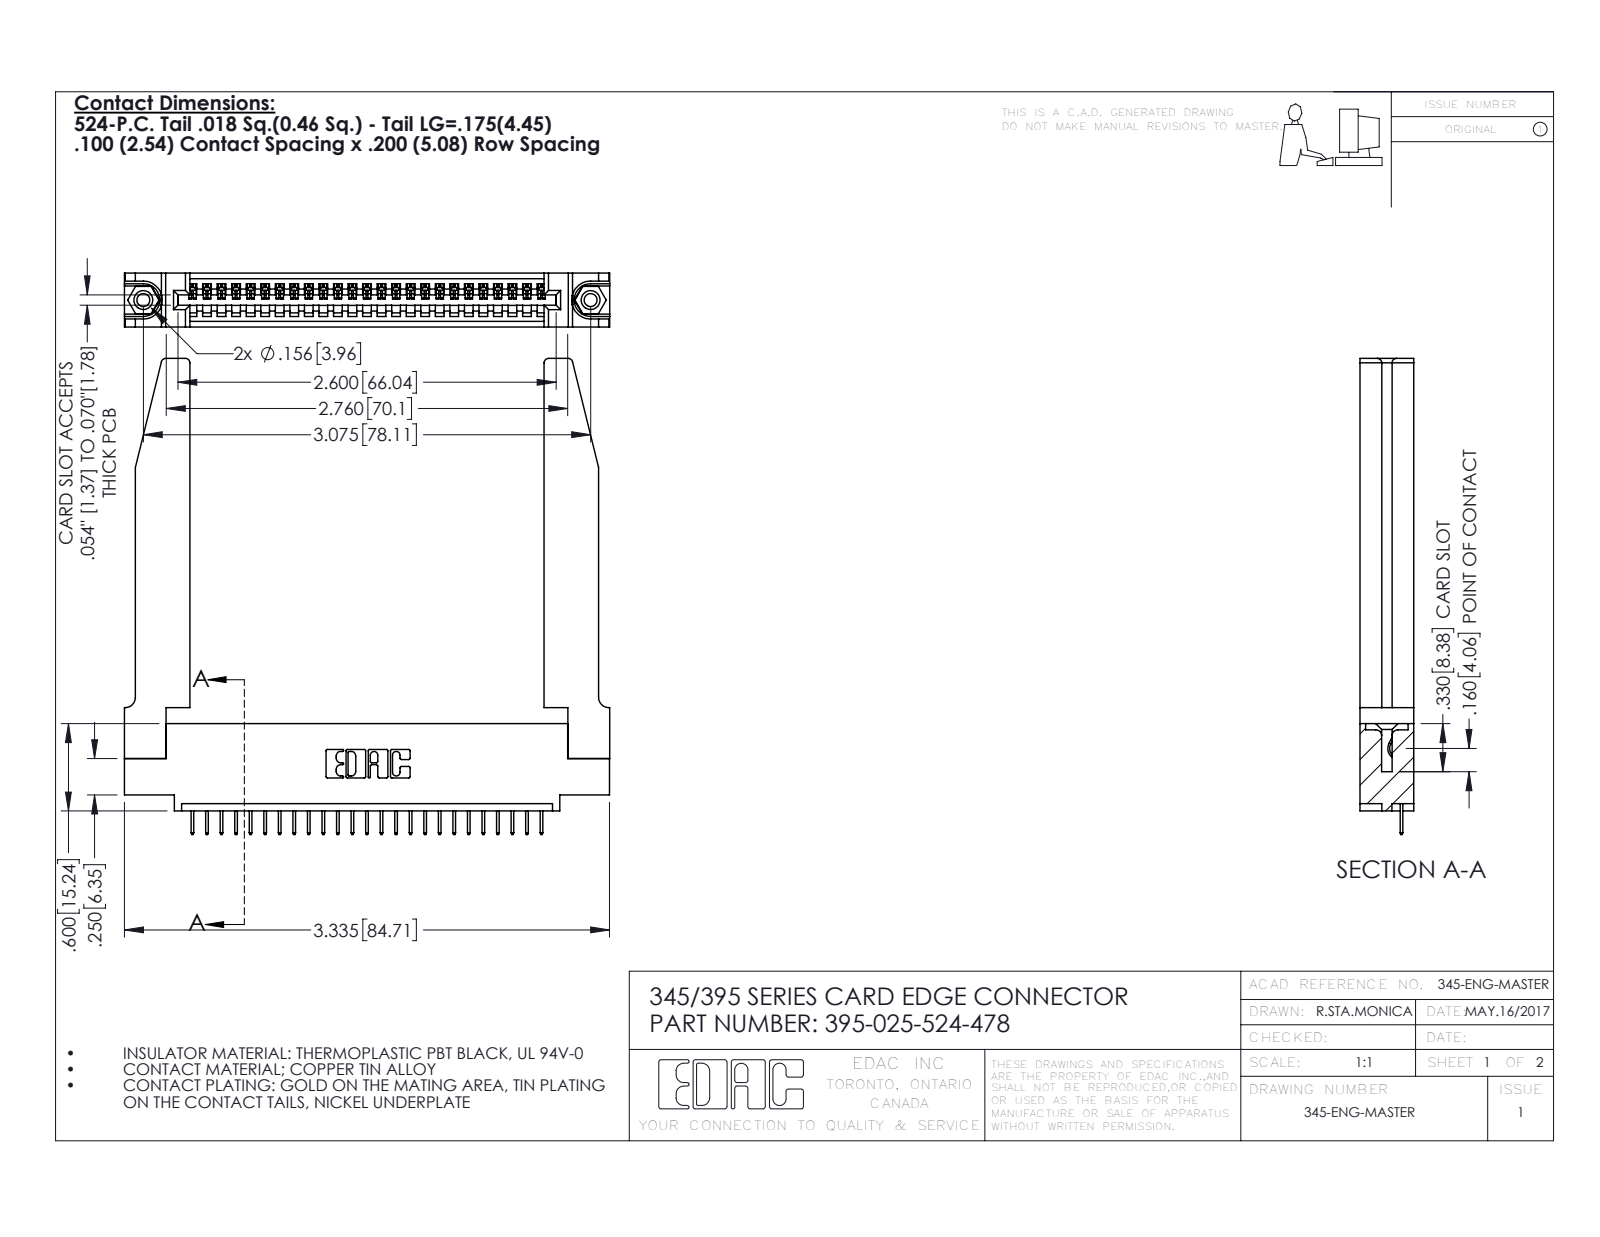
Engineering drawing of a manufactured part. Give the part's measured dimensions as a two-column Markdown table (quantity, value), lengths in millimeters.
| quantity | value |
| --- | --- |
| part name | 345-250-001_345-250-001-102; 345-220-078_345-220-078; 345-292-001_345-293-124; 345 Part_0.110 Offset - 0.156 Dia-TH (+1 more) |
| STEP written by | SolidWorks 2016 (CONFIG_CONTROL_DESIGN) |
| units | millimeters |
| bodies | 30 solids, 1914 faces (1376 planar, 486 cylindrical, 52 other) |
| overall size | 84.7 × 83.1 × 9.4 |
| volume | 15 500 mm³ |
| surface area | 16 660 mm² |
| round holes (diameter × count) | 2.3 × 2, 3.2 × 2, 4 × 2, 1.6 × 1 |
| round bosses / shafts (diameter × count) | 3.9 × 2 |
| partial cylindrical surfaces (radius × count) | 0.2 × 50, 0.3 × 22, 0.8 × 8, 0.2 × 6, 0.8 × 6, 0.7 × 3, 0.8 × 2, 1 × 2 |
| main face-to-face distances | 9.4, 1.8, 7.6, 5.1, 2.5, 6.9, 0.6, 3.8, 3.8, 5.7 |
| hole center spacings | 6.9, 72.1, 78.1 |
